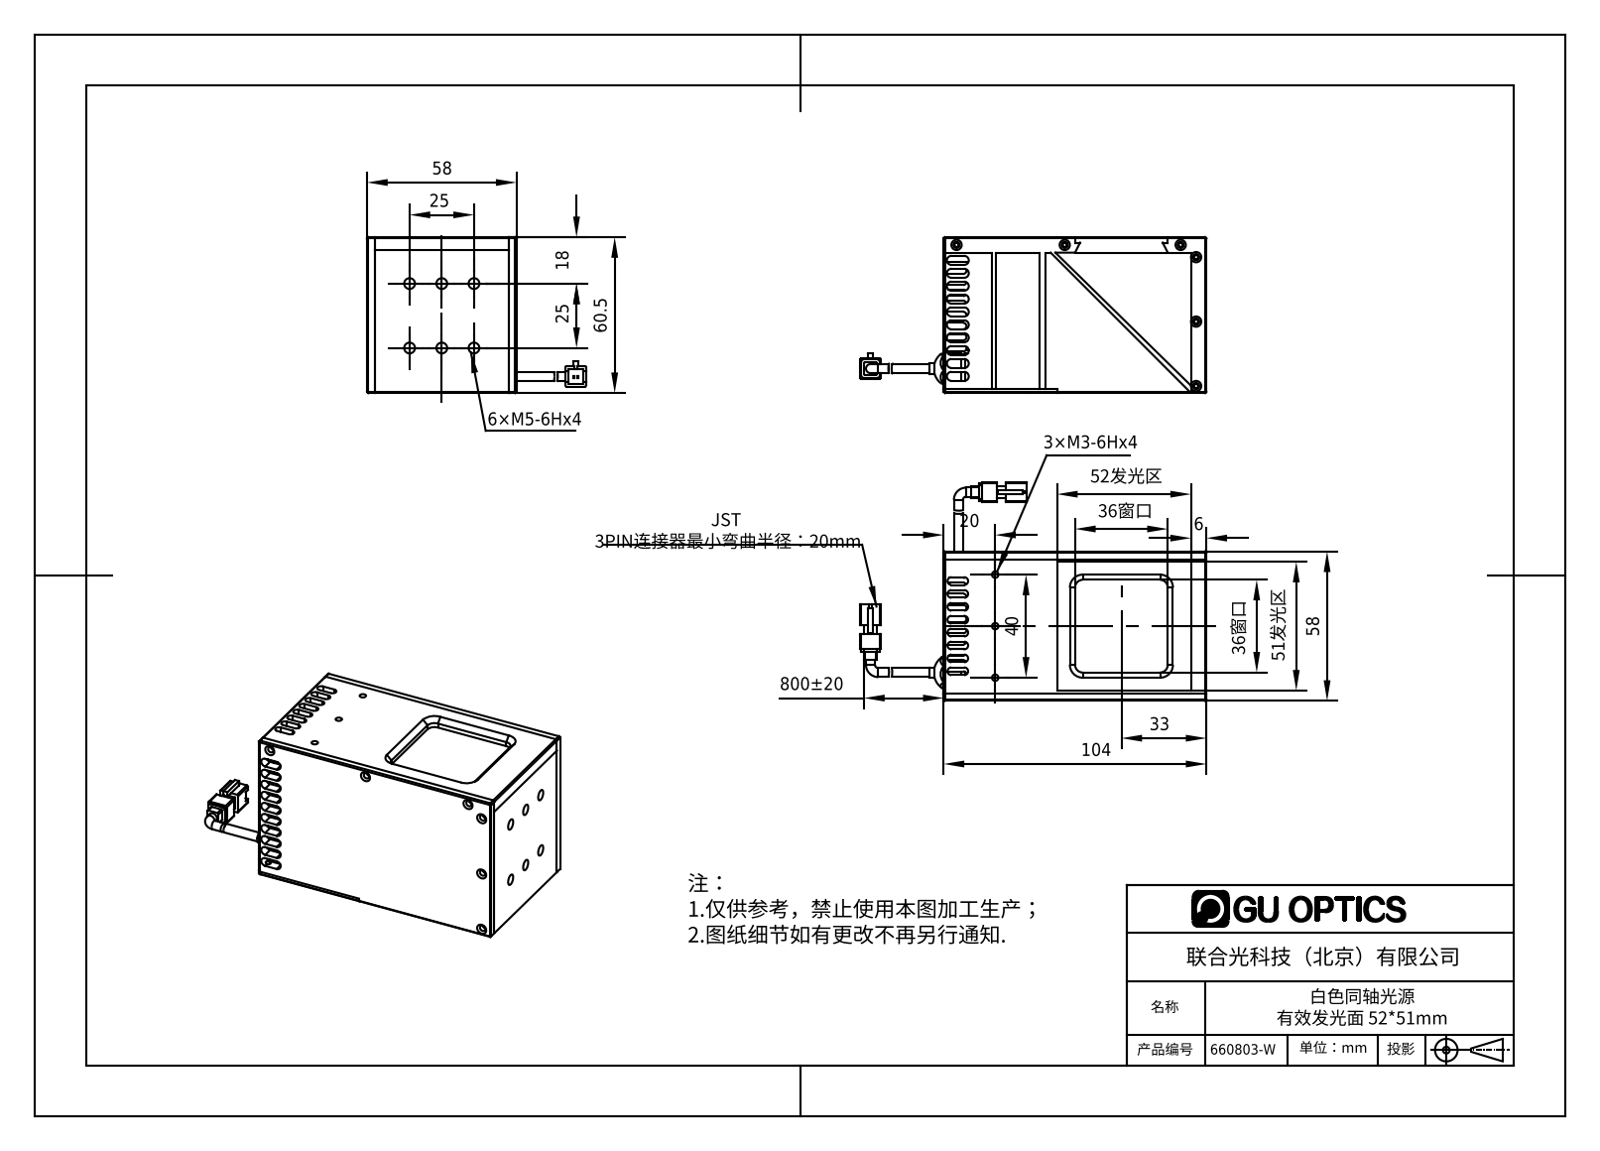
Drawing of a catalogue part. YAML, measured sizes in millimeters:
part_name: "白色同轴光源 有效发光面 5251mm"
step_written_by: "SolidWorks 2016 (AUTOMOTIVE_DESIGN)"
units: millimeters
bodies: {solids: 22, faces: 1568, planar: 921, cylindrical: 491, other: 156}
overall_size: [134.4, 60.7, 58]
volume: 118035
surface_area: 91224
round_holes:
  - {diameter: 1.6, count: 13}
  - {diameter: 2, count: 10}
  - {diameter: 2.4, count: 10}
  - {diameter: 4, count: 6}
  - {diameter: 4.2, count: 6}
  - {diameter: 2.2, count: 5}
  - {diameter: 2.5, count: 3}
  - {diameter: 6.8, count: 1}
round_bosses_or_shafts:
  - {diameter: 3.5, count: 2}
  - {diameter: 9.76, count: 1}
  - {diameter: 8, count: 1}
  - {diameter: 4, count: 1}
partial_cylinders:
  - {radius: 1.25, count: 20}
  - {radius: 1.75, count: 20}
  - {radius: 1.5, count: 16}
  - {radius: 0.5, count: 8}
  - {radius: 1, count: 4}
  - {radius: 3, count: 4}
  - {radius: 4, count: 1}
  - {radius: 6.25, count: 1}
face_to_face_distances: [4, 54, 2, 55, 1, 58, 3, 51, 58.5, 6]
hole_center_spacings: [25, 12.5, 20, 27.95, 30, 3.58, 5.51, 9.03]
